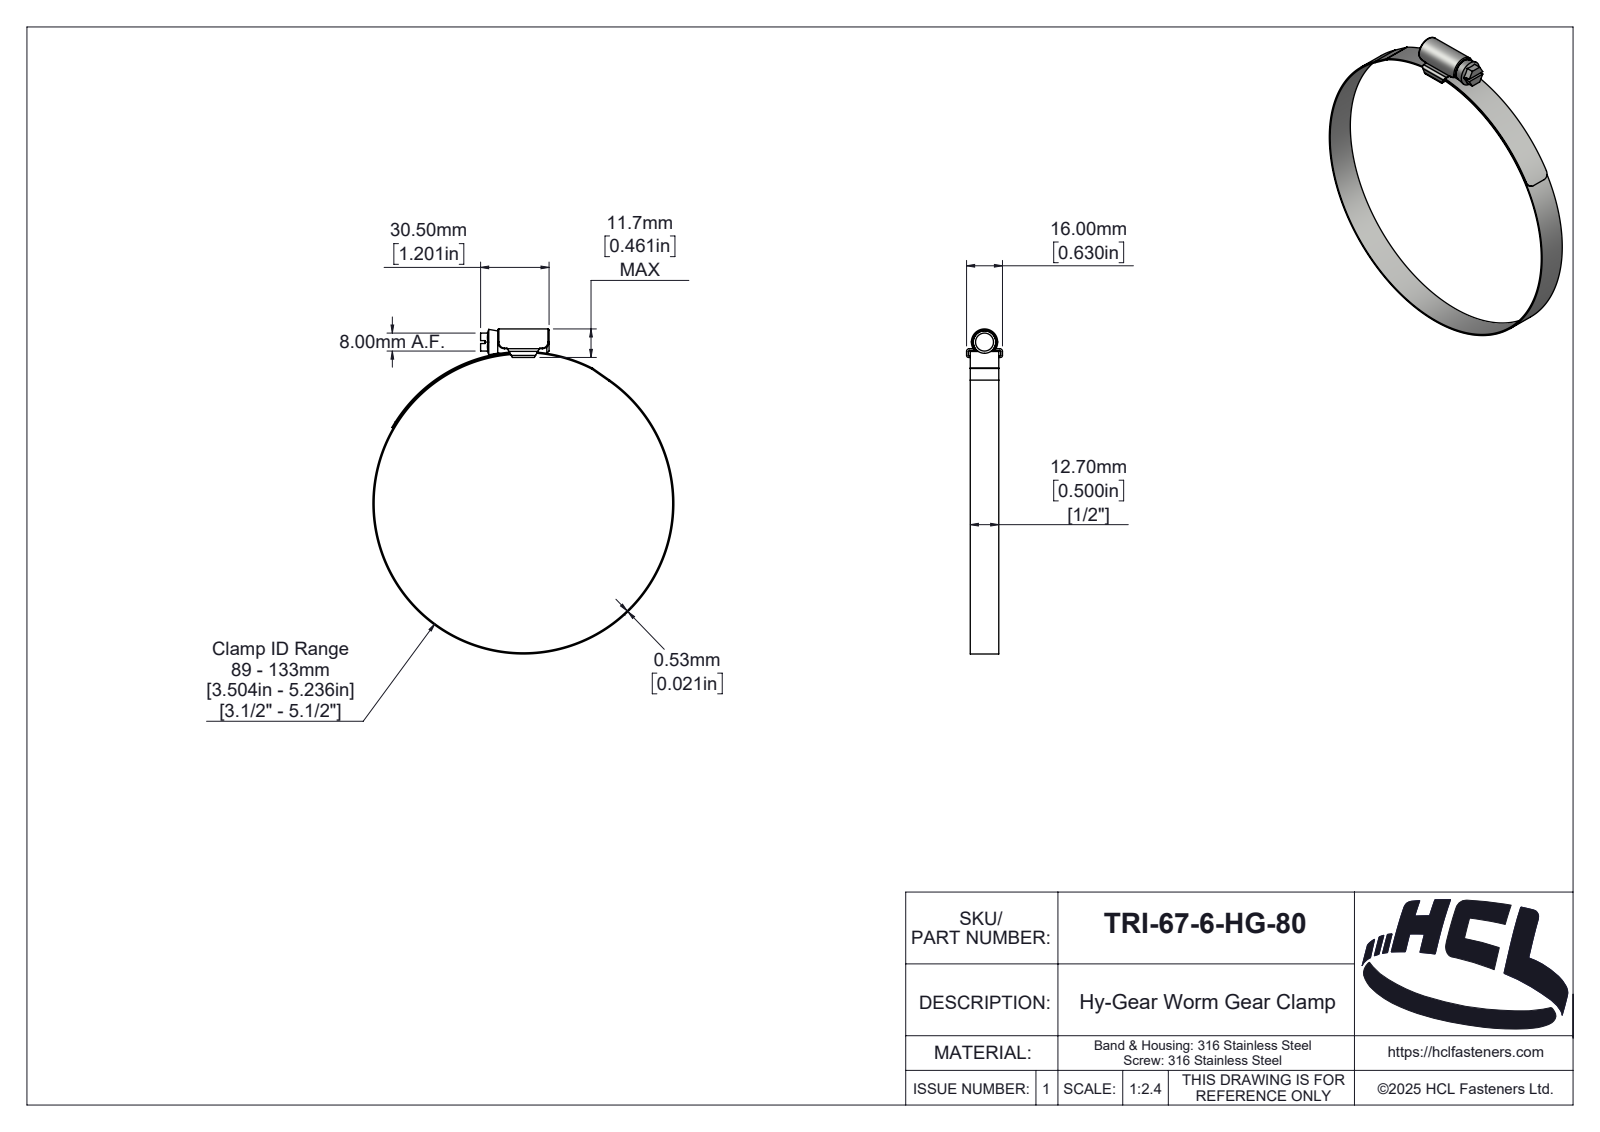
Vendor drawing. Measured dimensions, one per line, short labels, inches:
name: TRI-57-0-HG-80
written by: SolidWorks 2025 (AUTOMOTIVE_DESIGN)
unit: in
bodies: 3 solids, 189 faces (39 planar, 89 cylindrical, 61 other)
size: 5.698 × 5.278 × 0.63
volume: 0.384 in³; area: 24.61 in²
holes: 1× ⌀5.236
bosses: 1× ⌀5.278, 1× ⌀0.394
rounds: 6× R0.02, 4× R0.118, 2× R0.004, 2× R0.035, 2× R0.047, 1× R0.018, 1× R0.074, 1× R0.079
face distances: 0.5, 0.031, 0.122, 0.021, 0.091, 0.154, 1.201, 0.065, 0.565, 0.598
